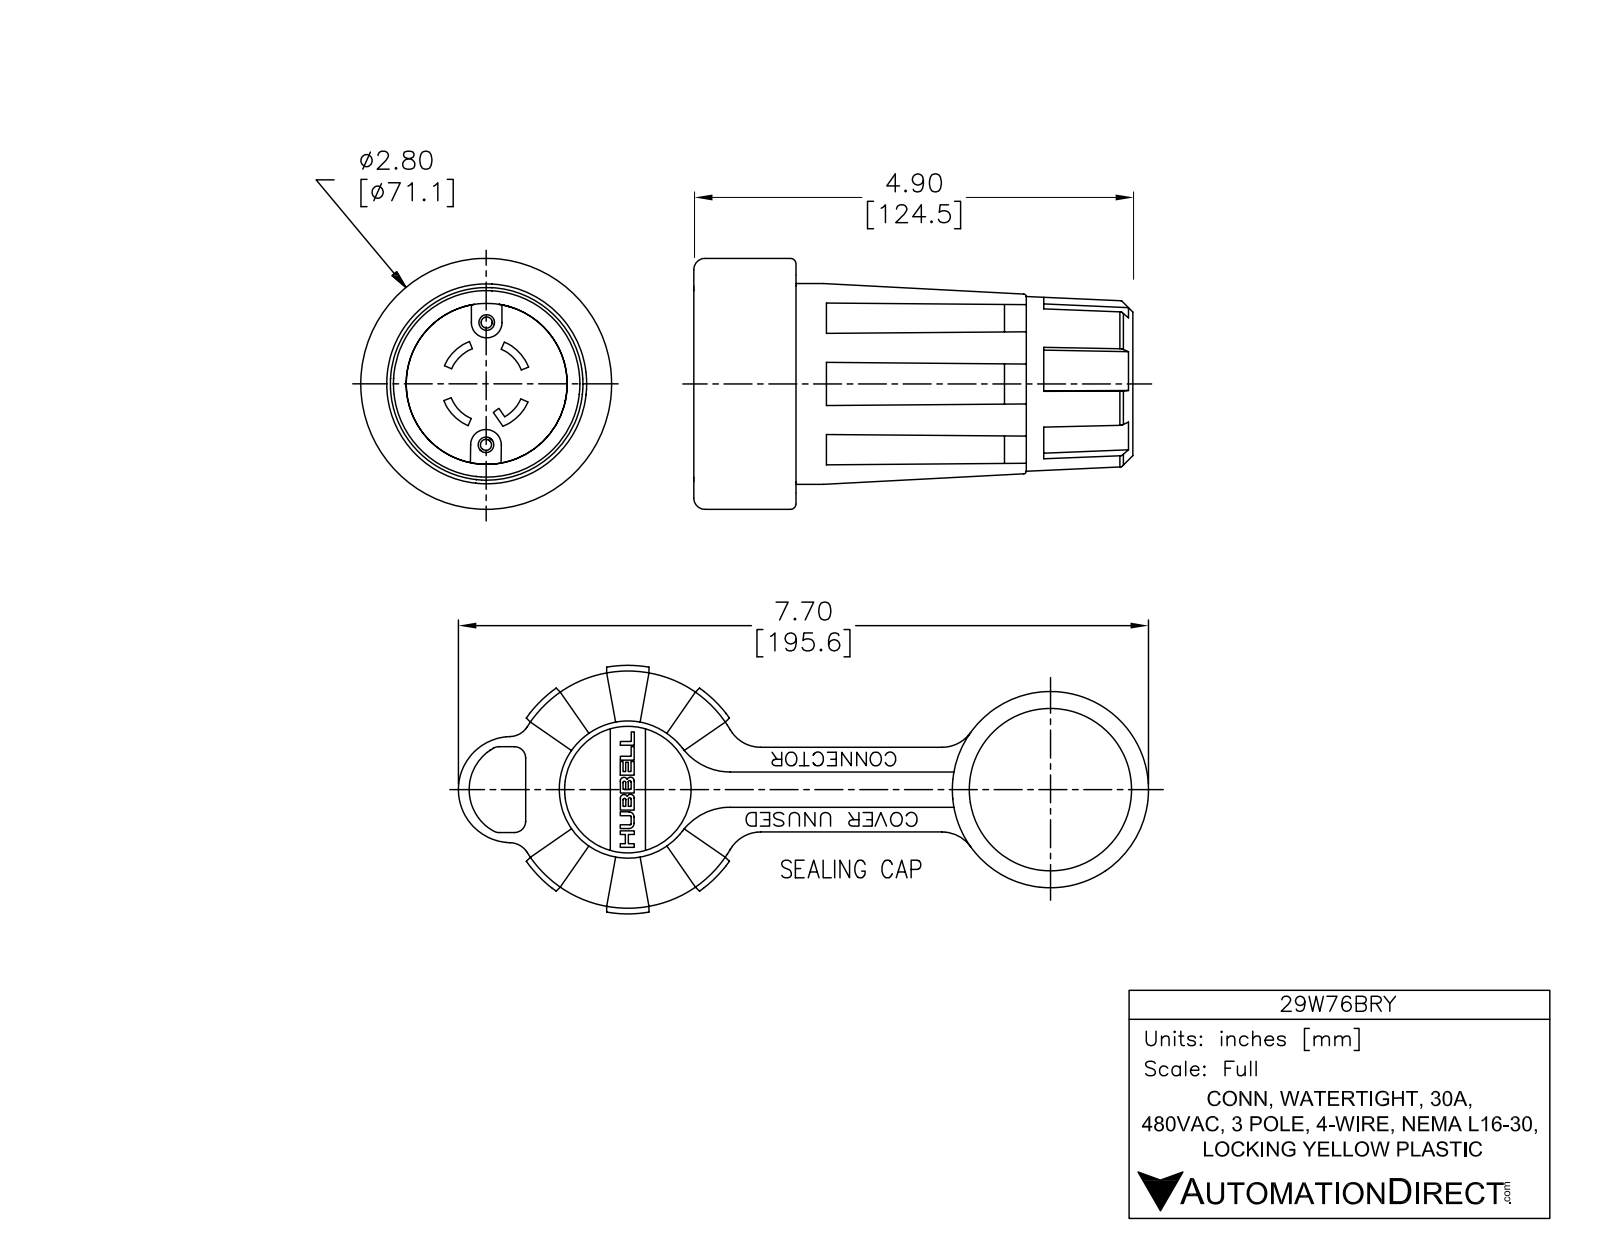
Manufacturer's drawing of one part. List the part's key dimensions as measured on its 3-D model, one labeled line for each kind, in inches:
Part name (STEP PRODUCT): 29W76BRY
STEP written by: SolidWorks 2013 (AUTOMOTIVE_DESIGN)
Units: inches
Bodies: 1 solid, 359 faces (137 planar, 98 cylindrical, 124 other)
Overall size (bounding box): 8.08 × 4.966 × 3.139
Volume: 20.17 in³ · Surface area: 104.7 in²
Round holes (diameter × count): ⌀0.95 ×1, ⌀1.82 ×1, ⌀1.86 ×1, ⌀2.345 ×1, ⌀2.805 ×1
Round bosses / shafts (diameter × count): ⌀0.2 ×2, ⌀2.76 ×1, ⌀2.755 ×1, ⌀2.43 ×1, ⌀2.25 ×1, ⌀1.975 ×1, ⌀1.415 ×1
Partial cylindrical surfaces — rounded edges, fillets, slot ends (radius × count): R0.015 ×16, R0.061 ×8, R0.25 ×6, R1.57 ×6, R0.1 ×2, R0.11 ×2, R0.4 ×1, R0.47 ×1
Main face-to-face distances: 0.08, 0.38, 0.67, 0.75, 0.06, 0.81, 0.14, 0.13, 2.685, 2.555
Hole centre spacings: 4.7
